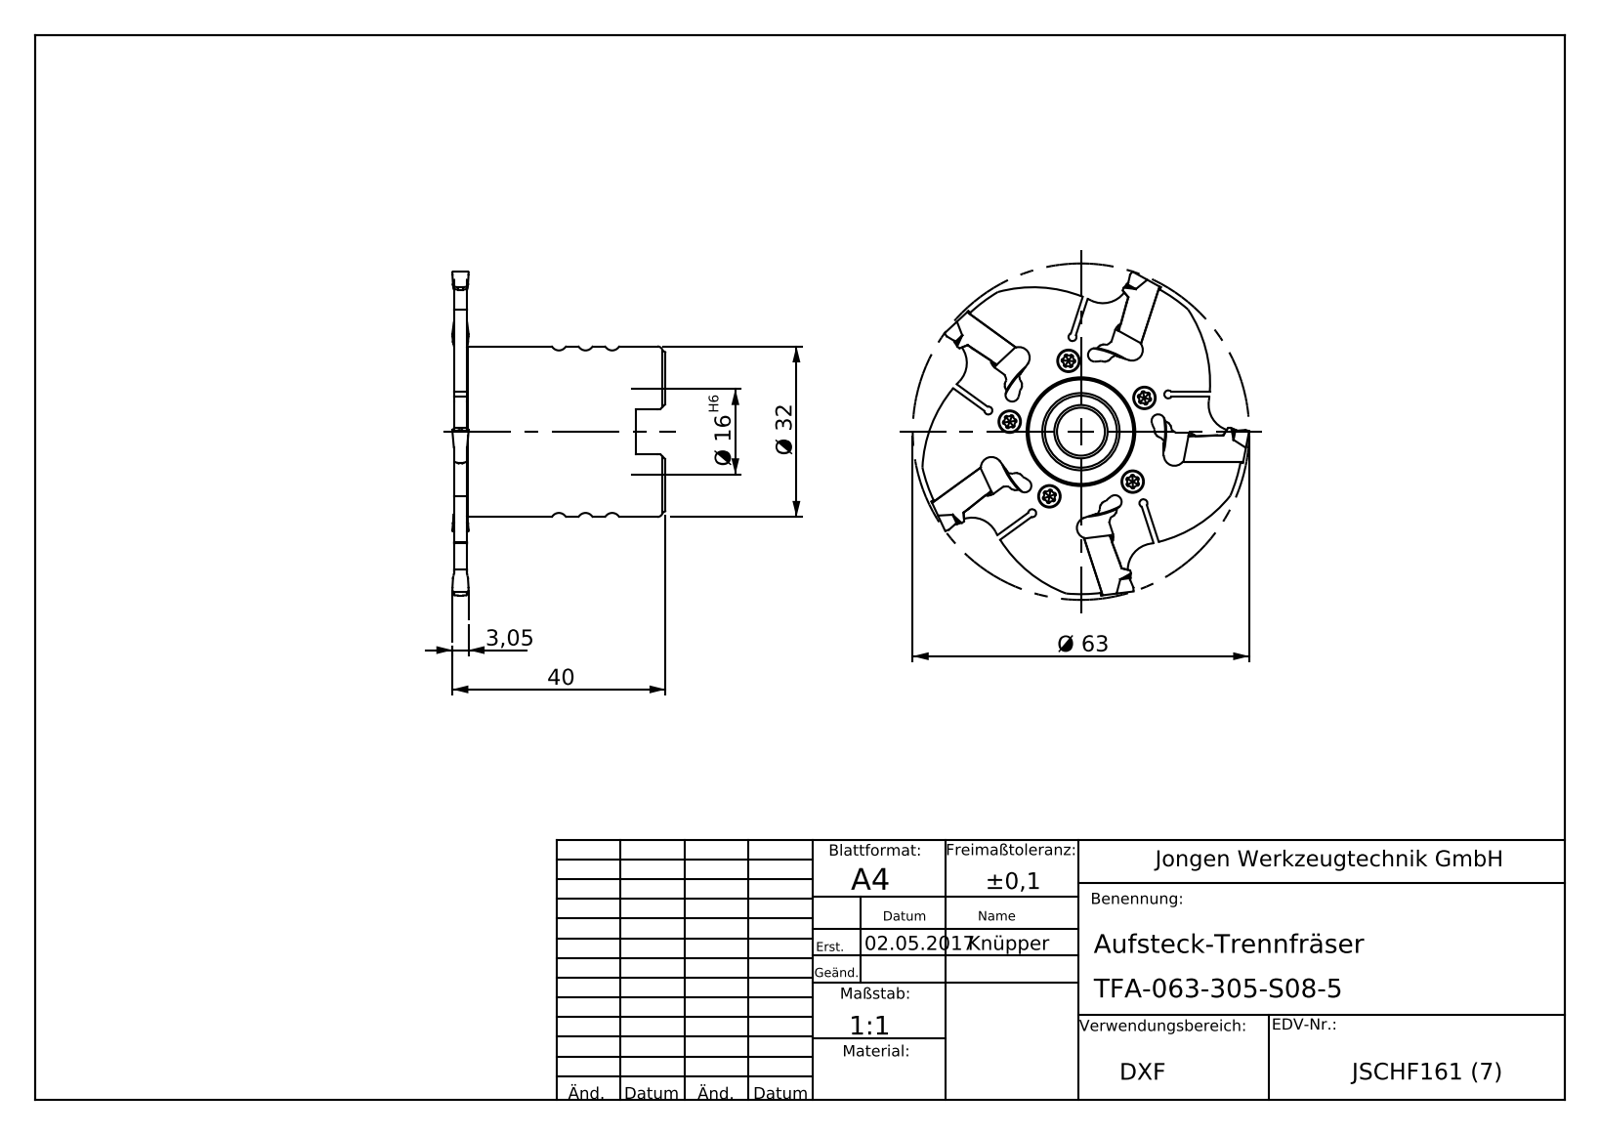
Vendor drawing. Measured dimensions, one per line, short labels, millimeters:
name: JSCHF161_1 pk; TFA-063-305-S08-5; JSCHF161 pk_Kontrolle
written by: SolidWorks 2018 (AUTOMOTIVE_DESIGN)
unit: mm
bodies: 2 solids, 209 faces (30 planar, 105 cylindrical, 74 other)
size: 63 × 63 × 40
volume: 30 967 mm³; area: 13 948 mm²
holes: 5× ⌀2.5, 5× ⌀3.2, 5× ⌀4.2, 1× ⌀9, 1× ⌀13.5, 1× ⌀16, 1× ⌀16.15, 1× ⌀16.3, 1× ⌀20, 1× ⌀32.82
bosses: 1× ⌀63, 1× ⌀32
rounds: 15× R1, 10× R2, 5× R1.25, 5× R4.64, 5× R7.14
face distances: 3.05, 2.78, 2.77, 2.5, 36.95, 37.22, 39.72, 40, 20, 5.6
hole spacings: 13.5, 15.87, 25.68, 25.69, 25.66, 25.67, 15.83, 15.9
